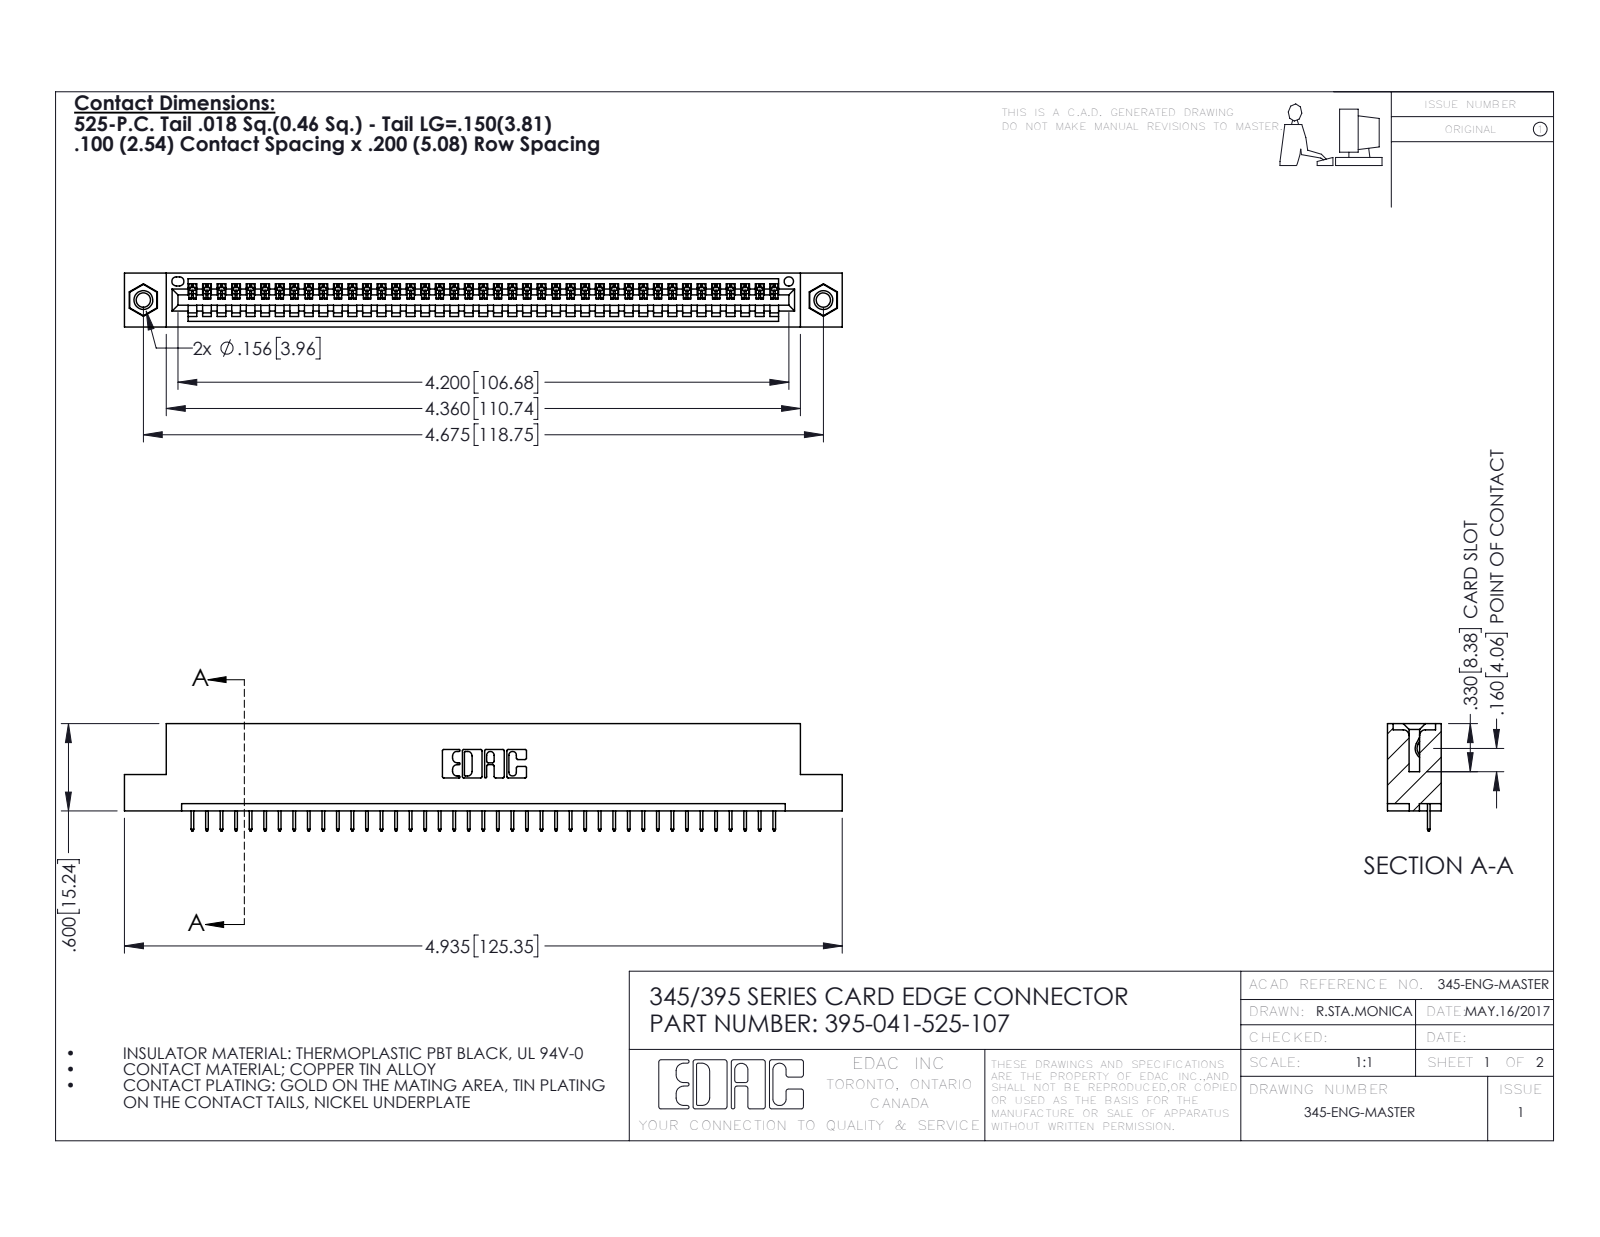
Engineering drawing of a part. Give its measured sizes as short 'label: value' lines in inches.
name: 345-292-001_345-293-125; 345-250-001_345-250-005-103; 345 Part_Flush Mounting Lugs - 0.156 Dia-TI; 395-041-525-107
written by: SolidWorks 2020 (CONFIG_CONTROL_DESIGN)
unit: in
bodies: 44 solids, 2728 faces (1998 planar, 714 cylindrical, 16 other)
size: 4.935 × 0.737 × 0.37
volume: 0.715 in³; area: 23.3 in²
holes: 2× ⌀0.098, 2× ⌀0.125, 2× ⌀0.156, 1× ⌀0.064
bosses: 2× ⌀0.155
rounds: 82× R0.006, 22× R0.01, 6× R0.007, 6× R0.031, 3× R0.026, 2× R0.031, 2× R0.04, 1× R0.014
face distances: 0.072, 0.298, 0.37, 0.2, 0.098, 0.272, 0.025, 0.225, 0.072, 0.149
hole spacings: 0.27, 4.439, 4.675
